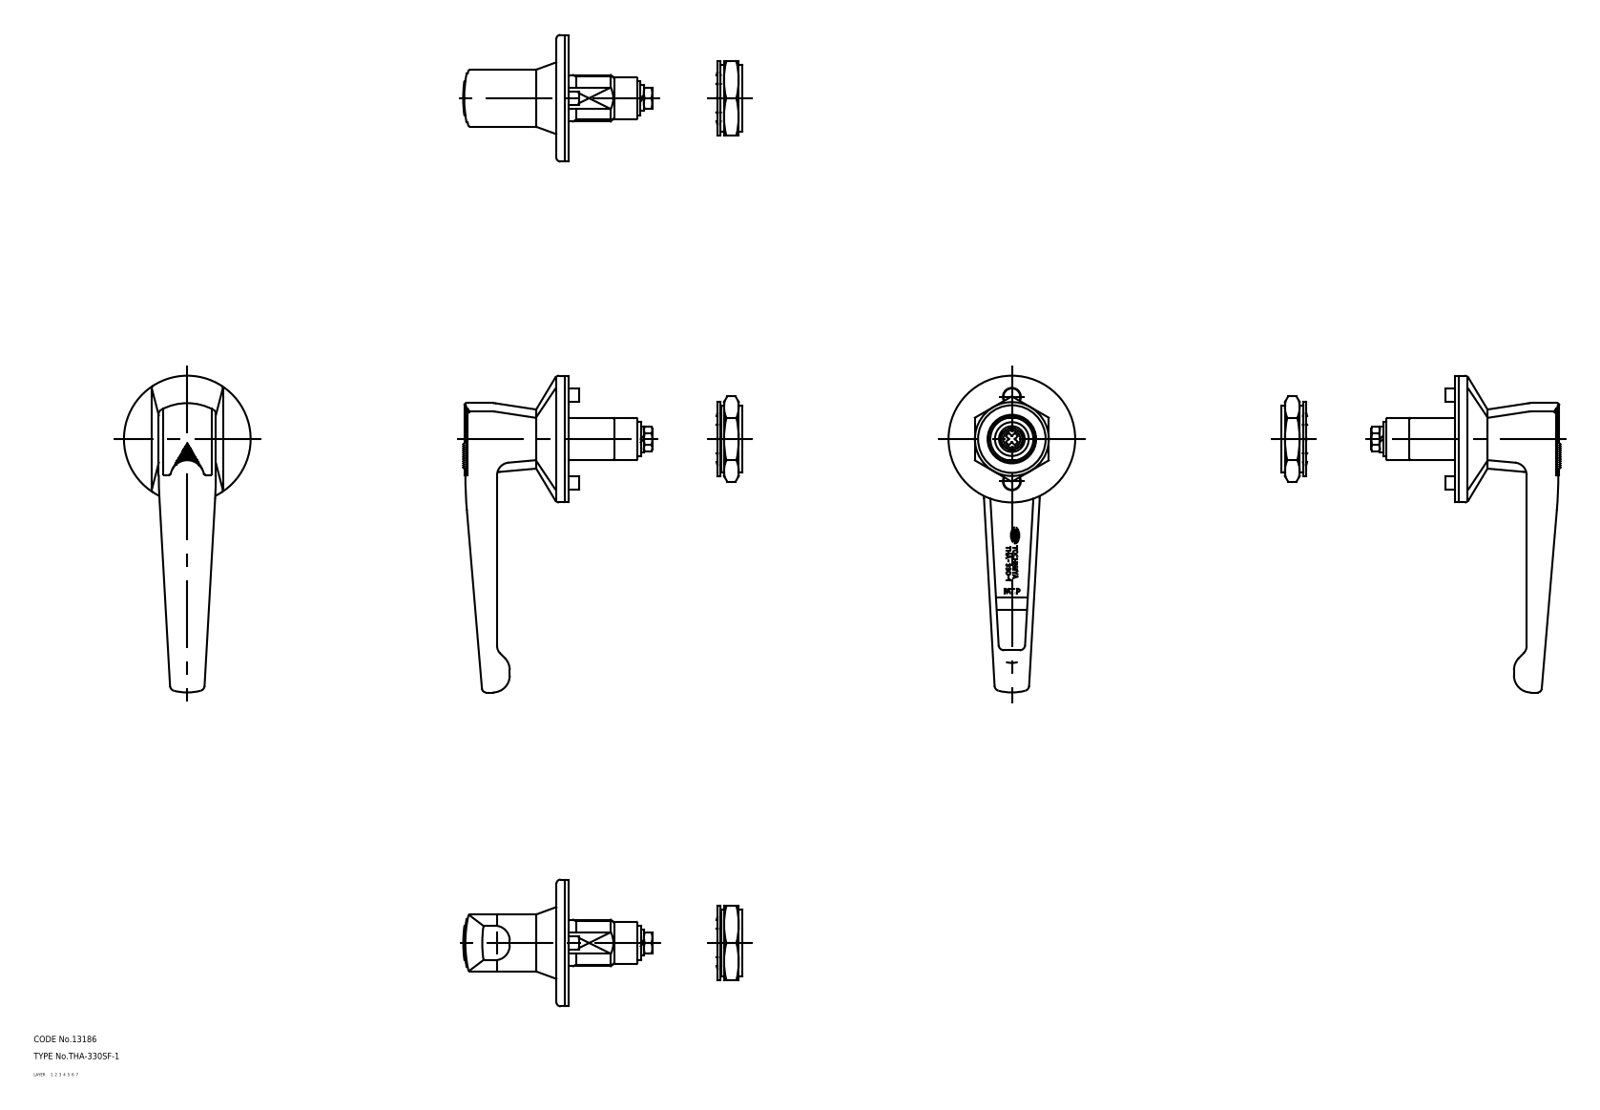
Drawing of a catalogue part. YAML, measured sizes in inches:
part_name: "washer_B; washer_A; spacer; packing (+5 more)"
step_written_by: "CADfix (AUTOMOTIVE_DESIGN)"
units: inches
bodies: {solids: 8, faces: 296, planar: 0, cylindrical: 0, other: 296}
overall_size: [5.906, 3.526, 2.362]
volume: 5.272
surface_area: 59.28
